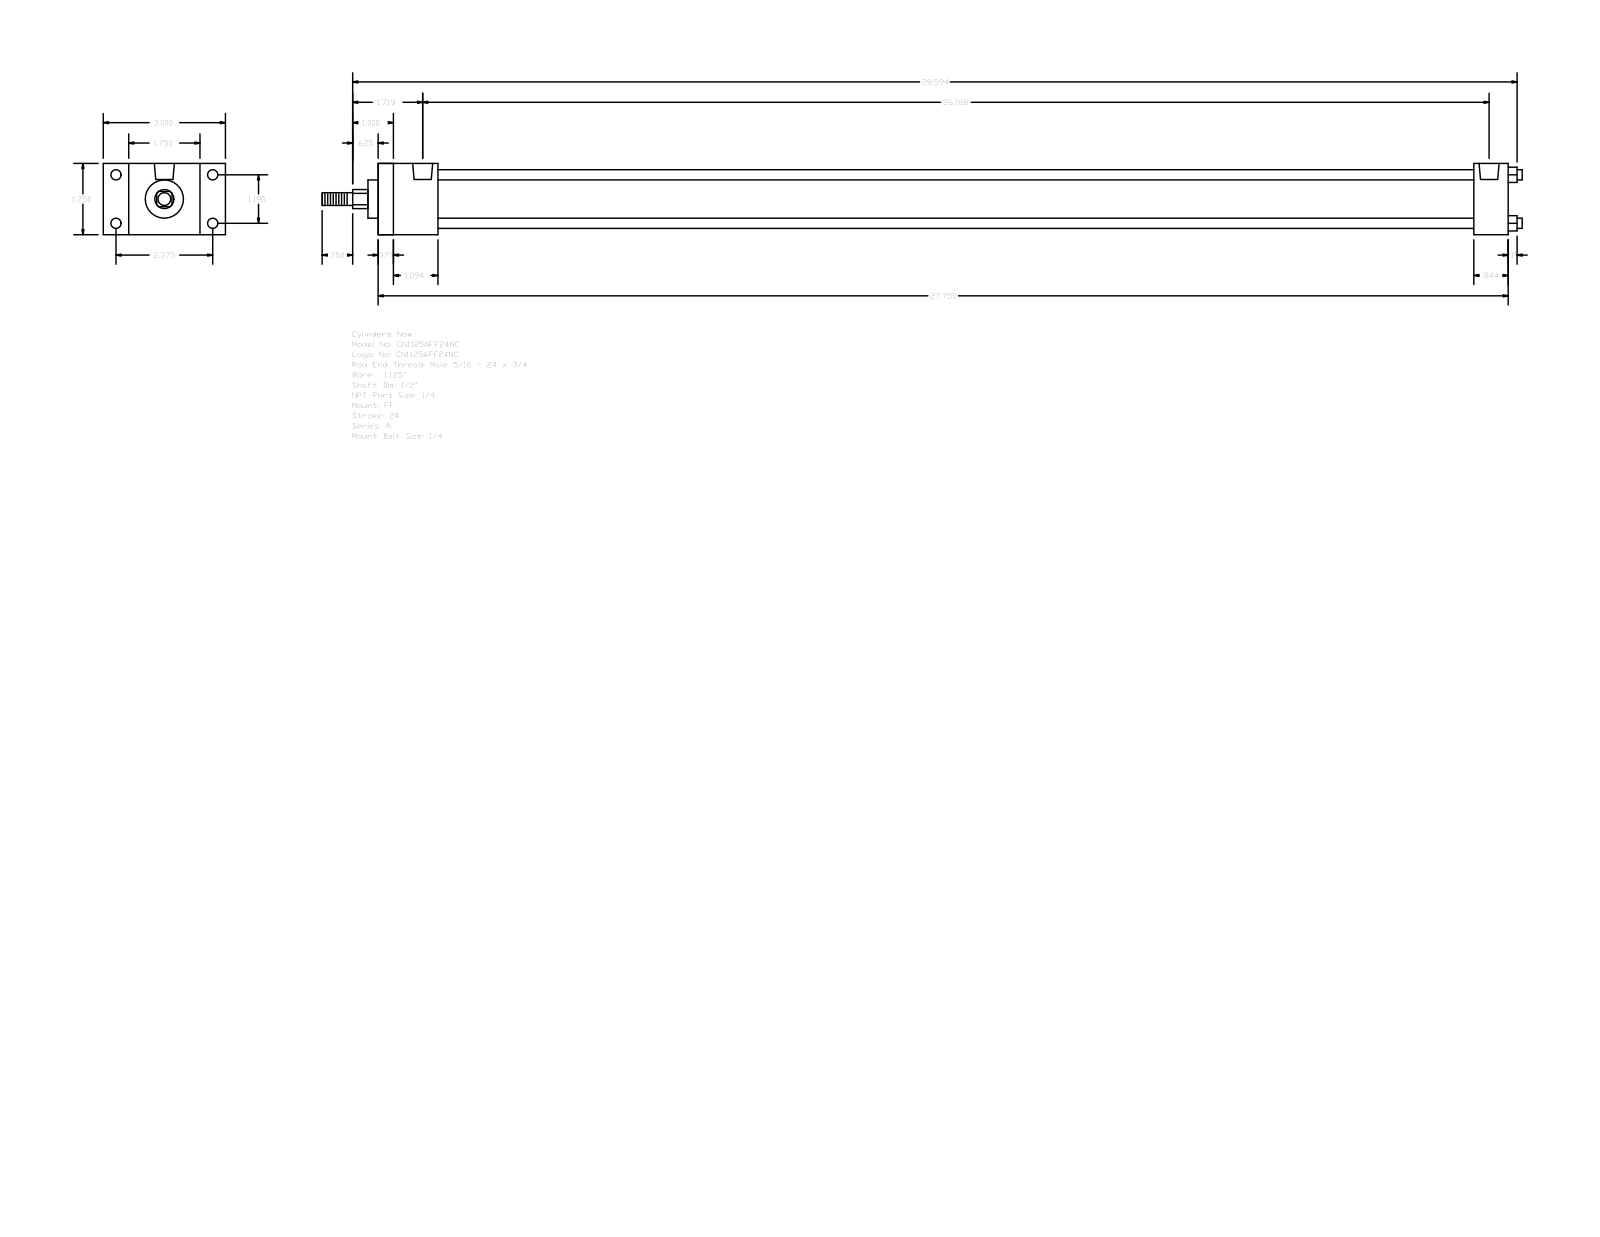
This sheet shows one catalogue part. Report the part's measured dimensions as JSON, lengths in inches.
{"part_name": "A_FF__0112_0.5", "step_written_by": "GSSL Pune (CONFIG_CONTROL_DESIGN)", "units": "inches", "bodies": {"solids": 0, "faces": 92, "planar": 64, "cylindrical": 28, "other": 0}, "overall_size": [29.469, 3, 1.75], "round_holes": [[0.219, 4], [0.25, 4], [0.492, 2]], "round_bosses_or_shafts": [[0.25, 4], [1.255, 1], [0.937, 1], [0.5, 1], [0.313, 1]], "partial_cylinders_radius": [[0.234, 1]], "face_to_face_distances": [1.75, 27.75, 0.375, 27.375, 0.625, 26.906, 26.531, 0.844, 1.469, 1.094], "hole_center_spacings": [1.19, 2.375, 2.656, 26.063, 0.062, 0.063, 26.125, 26.125]}
